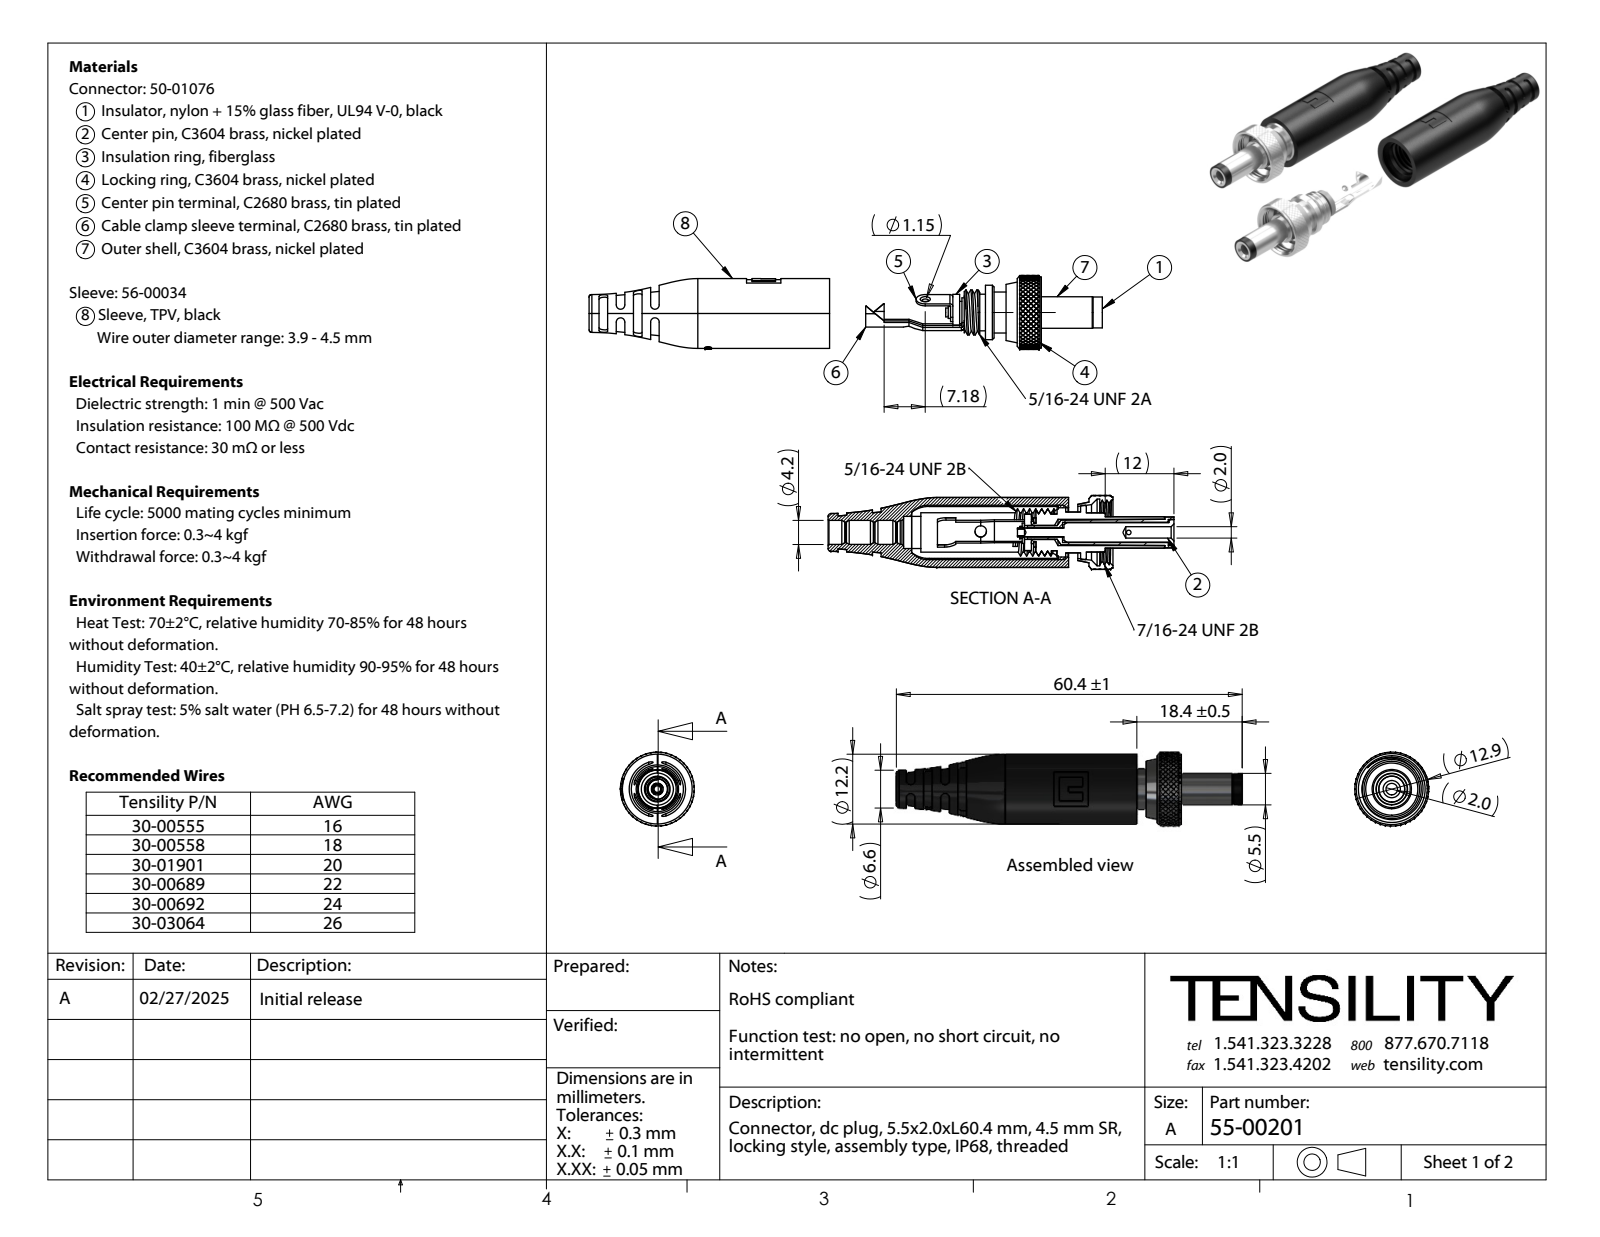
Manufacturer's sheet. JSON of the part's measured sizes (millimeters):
{"part_name": "50-01076_pin_2.0??; 50-01076_Outer tube; 50-01076_Cable clamp sleeve terminal; Copy of 50-01077_Floating locking ring_Step (+8 more)", "step_written_by": "SolidWorks 2021 (CONFIG_CONTROL_DESIGN)", "units": "millimeters", "bodies": {"solids": 9, "faces": 399, "planar": 128, "cylindrical": 146, "other": 125}, "overall_size": [60.99, 12.9, 12.9], "volume_mm3": 3484, "surface_area_mm2": 7088, "round_holes": [[1.15, 2], [0.8, 1], [1.6, 1], [2, 1], [2.01, 1], [2.45, 1], [2.5, 1], [3.35, 1], [3.55, 1], [4.55, 1], [4.6, 1], [5.6, 1]], "round_bosses_or_shafts": [[12.9, 1], [12.4, 1], [12.2, 1], [7.85, 1], [7.15, 1], [6.85, 1], [6.4, 1], [5.5, 1]], "partial_cylinders_radius": [[0.75, 8], [0.2, 4], [1.57, 2], [6.1, 2], [0.1, 1], [0.4, 1], [0.5, 1], [0.6, 1]], "face_to_face_distances": [29.84, 0.4, 1.5, 4.1, 1.6, 5.11, 3.7, 1.41, 1.7, 3.41]}
